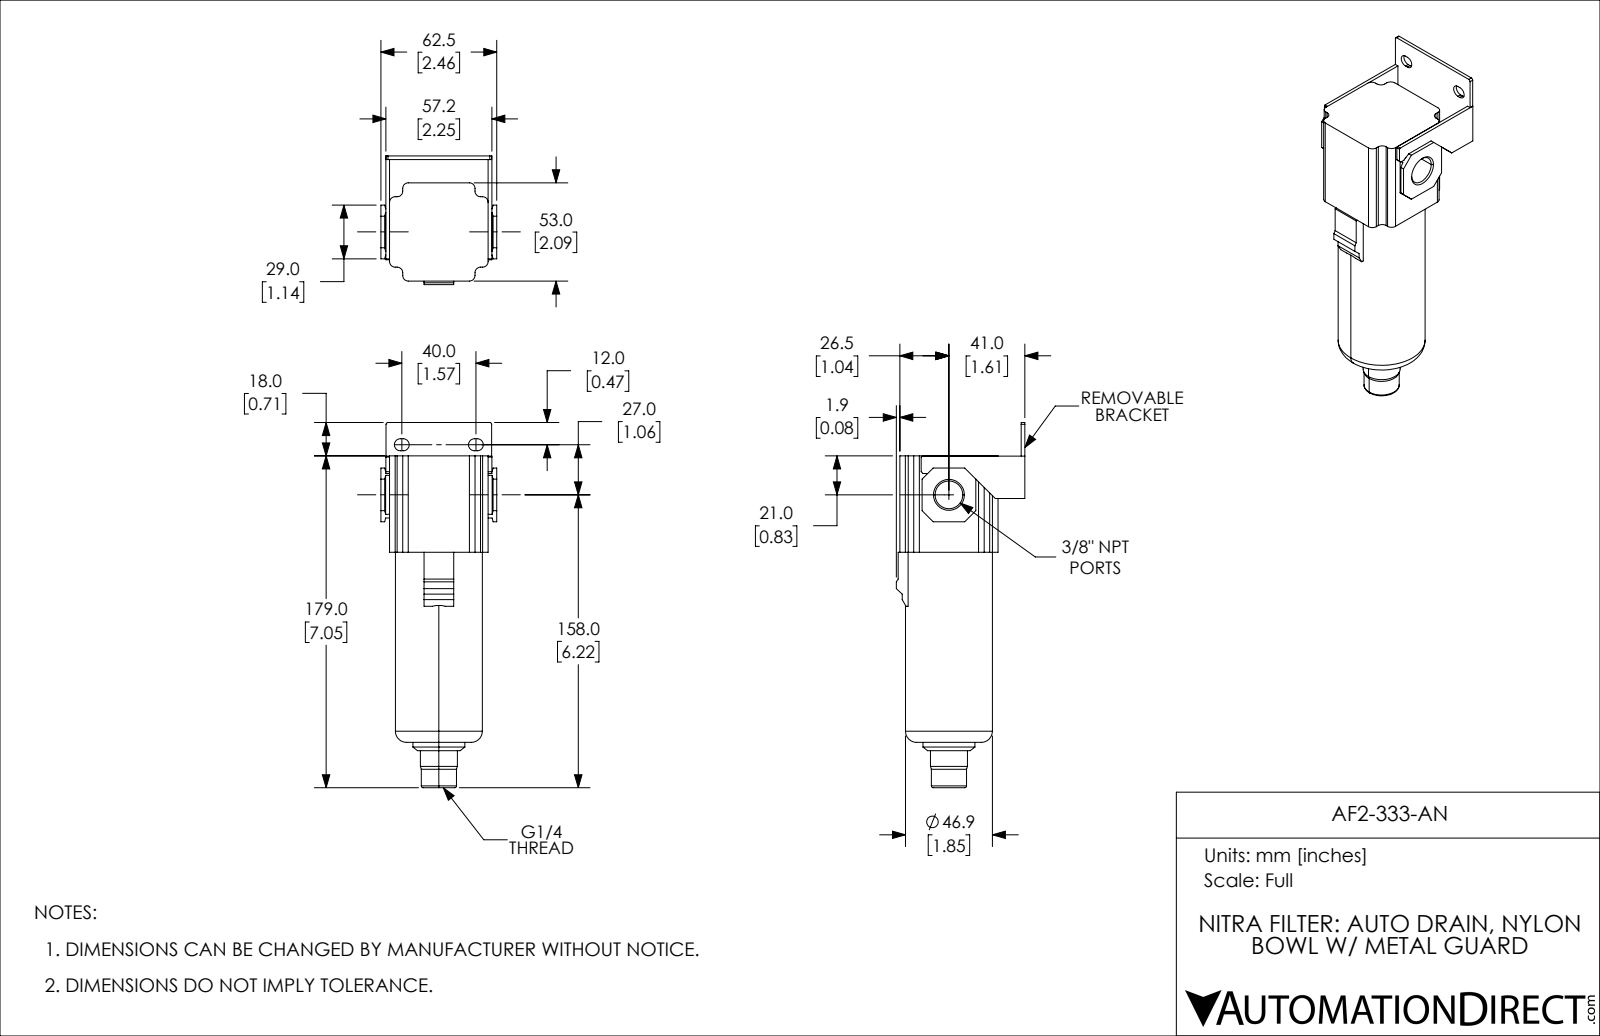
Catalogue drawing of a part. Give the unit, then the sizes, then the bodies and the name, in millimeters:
Units: millimetres
Overall size (bounding box): 197 × 69.42 × 62.5
Round holes (diameter × count): ⌀8.57 ×1, ⌀14.95 ×1
Round bosses / shafts (diameter × count): ⌀46.9 ×1, ⌀28 ×1, ⌀20 ×1, ⌀19 ×1
Partial cylindrical surfaces — rounded edges, fillets, slot ends (radius × count): R3 ×12, R3.25 ×4, R1 ×2
Main face-to-face distances: 2, 12.5, 14.5, 67.5, 65.5, 53, 55.2, 53.2, 2.65, 4.65
Volume: 329 171 mm³ · Surface area: 42 160 mm²
Bodies: 1 solid, 137 faces (91 planar, 32 cylindrical, 14 other)
Part name (STEP PRODUCT): AF2-333-AN
STEP written by: SolidWorks 2019 (CONFIG_CONTROL_DESIGN)
